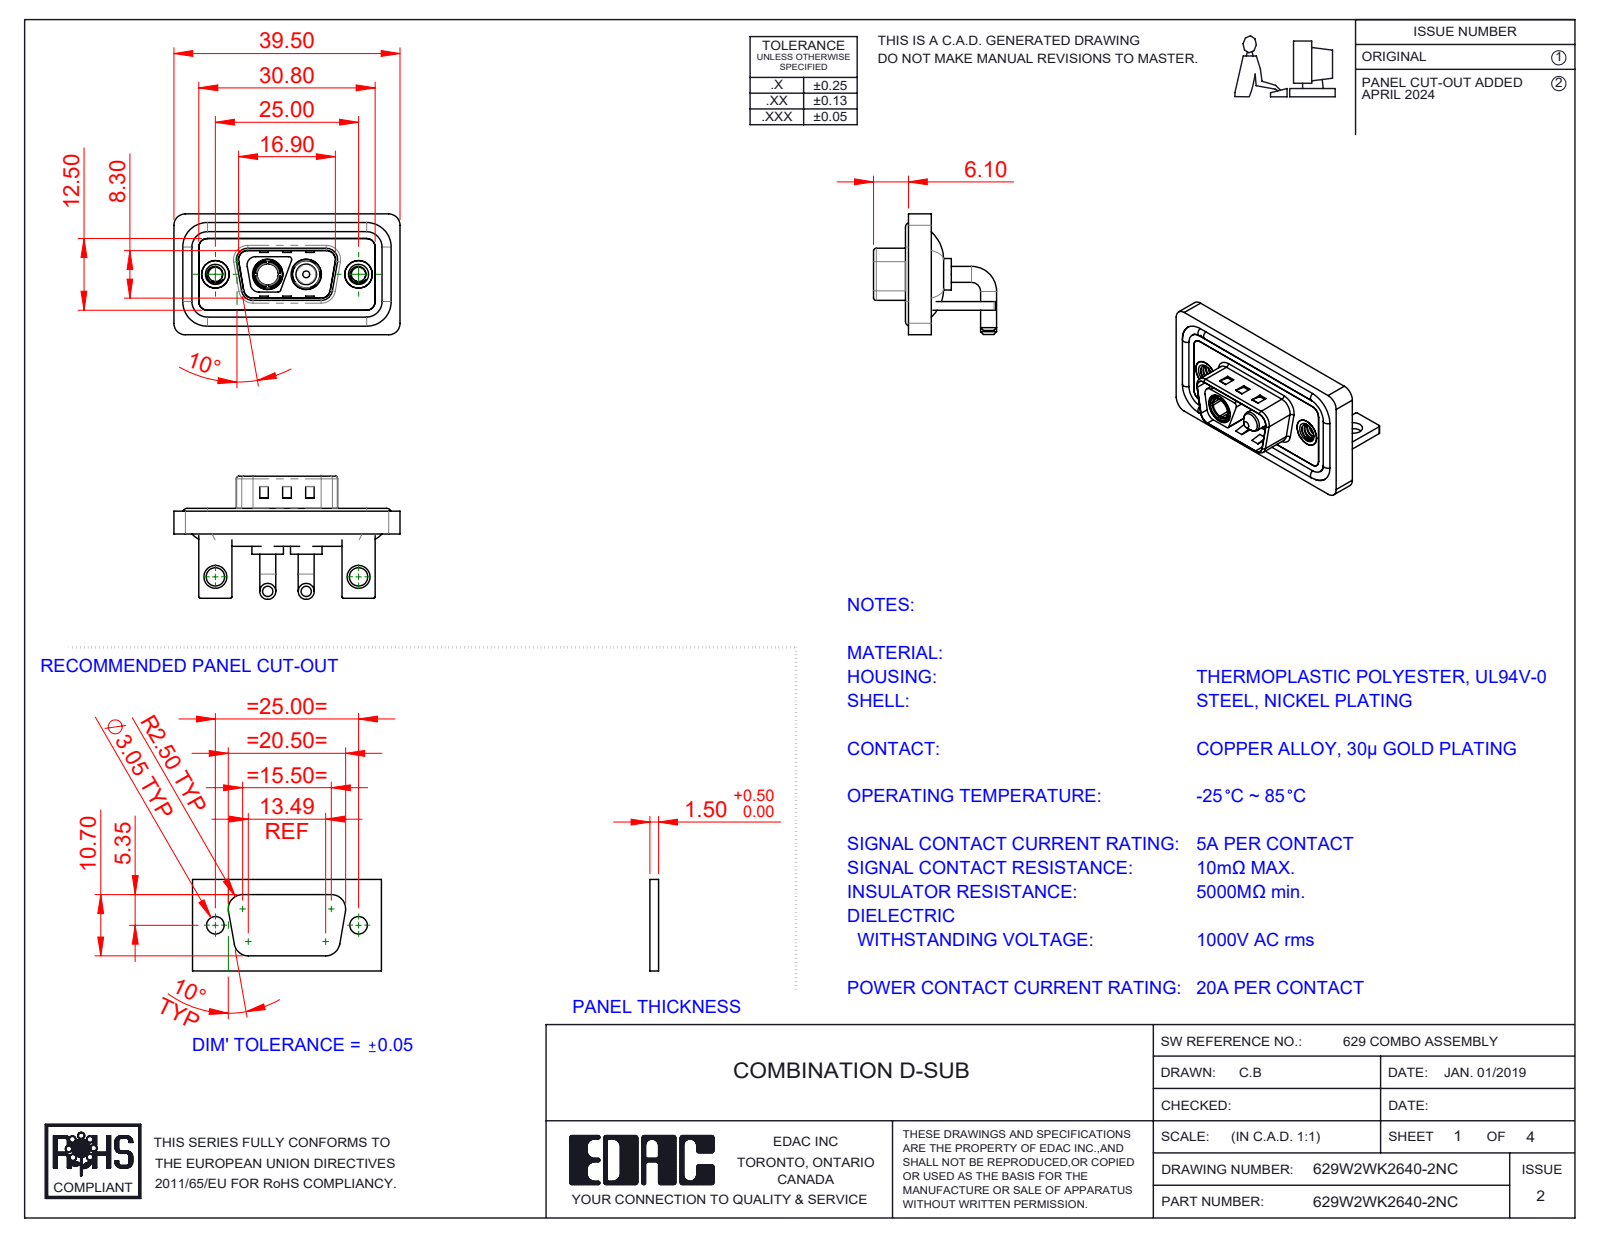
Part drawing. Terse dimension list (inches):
name: 629Combo Housing_2WK2; 629Combo Shell Front_09 Contacts; 629W2WK2640-2NC; 629Combo Waterproof Housing_09 Contacts (+5 more)
written by: SolidWorks 2023 (CONFIG_CONTROL_DESIGN)
unit: in
bodies: 13 solids, 580 faces (209 planar, 249 cylindrical, 122 other)
size: 1.555 × 0.846 × 0.831
volume: 0.302 in³; area: 12.59 in²
holes: 2× ⌀0.098, 2× ⌀0.126, 2× ⌀0.157, 2× ⌀0.189, 2× ⌀0.191, 2× ⌀0.197, 2× ⌀0.209, 1× ⌀0.146
bosses: 4× ⌀0.11, 4× ⌀0.063, 2× ⌀0.217, 2× ⌀0.205, 2× ⌀0.193, 2× ⌀0.187, 2× ⌀0.148, 1× ⌀0.195
rounds: 20× R0.059, 19× R0.079, 16× R0.01, 11× R0.02, 8× R0.063, 4× R0.024, 4× R0.026, 4× R0.035
face distances: 0.016, 0.059, 0.114, 0.031, 0.043, 0.047, 0.083, 0.063, 0.146, 0.098
hole spacings: 0.36, 0.624, 0.984, 0.265
